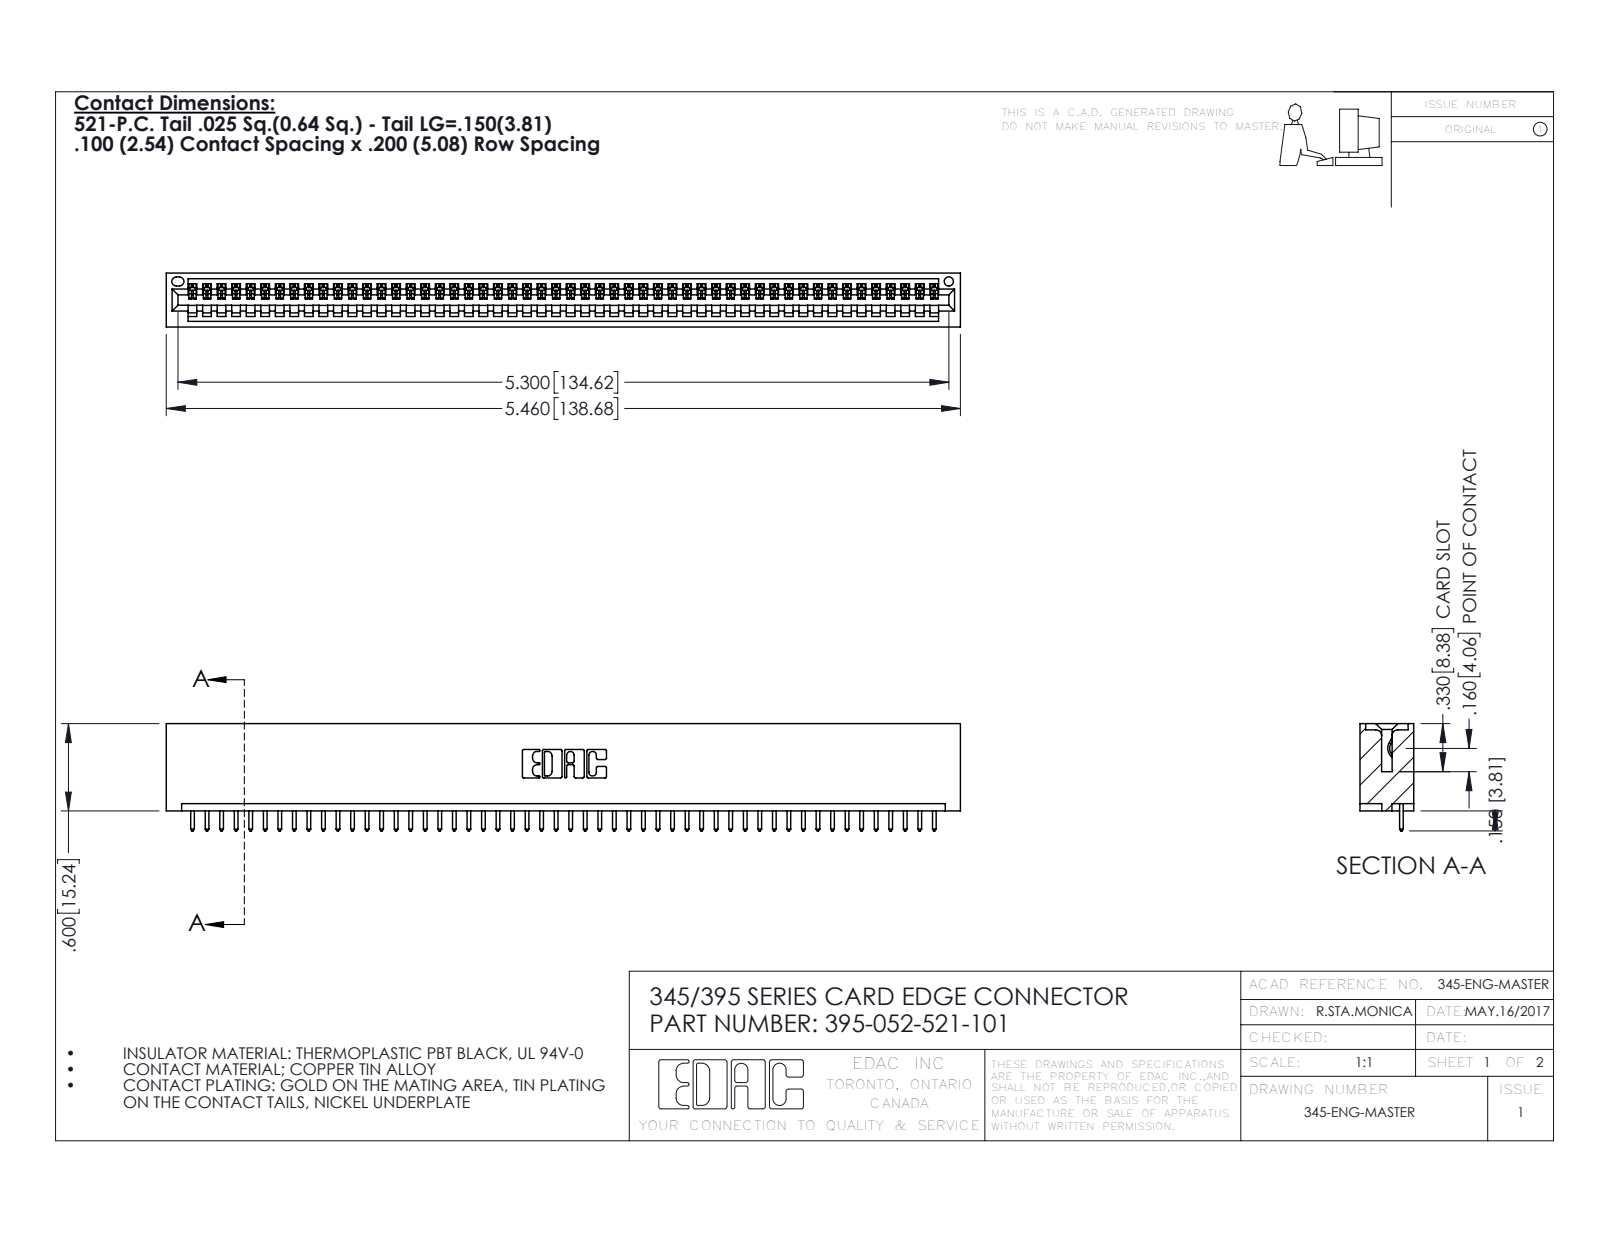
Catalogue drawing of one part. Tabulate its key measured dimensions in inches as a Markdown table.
| quantity | value |
| --- | --- |
| part name | 345-292-001_345-293-121; 395-052-521-101; 345 Part_No Mounting Lugs |
| STEP written by | SolidWorks 2016 (CONFIG_CONTROL_DESIGN) |
| units | inches |
| bodies | 53 solids, 3134 faces (2156 planar, 978 cylindrical, 0 other) |
| overall size | 5.46 × 0.737 × 0.37 |
| volume | 0.835 in³ |
| surface area | 27.81 in² |
| round holes (diameter × count) | 0.064 × 1 |
| partial cylindrical surfaces (radius × count) | 0.006 × 104, 0.01 × 104, 0.01 × 22, 0.007 × 6, 0.031 × 6, 0.026 × 3, 0.031 × 2, 0.04 × 2 |
| main face-to-face distances | 0.298, 0.072, 0.37, 0.2, 0.098, 0.272, 0.025, 0.225, 0.149, 0.072 |
